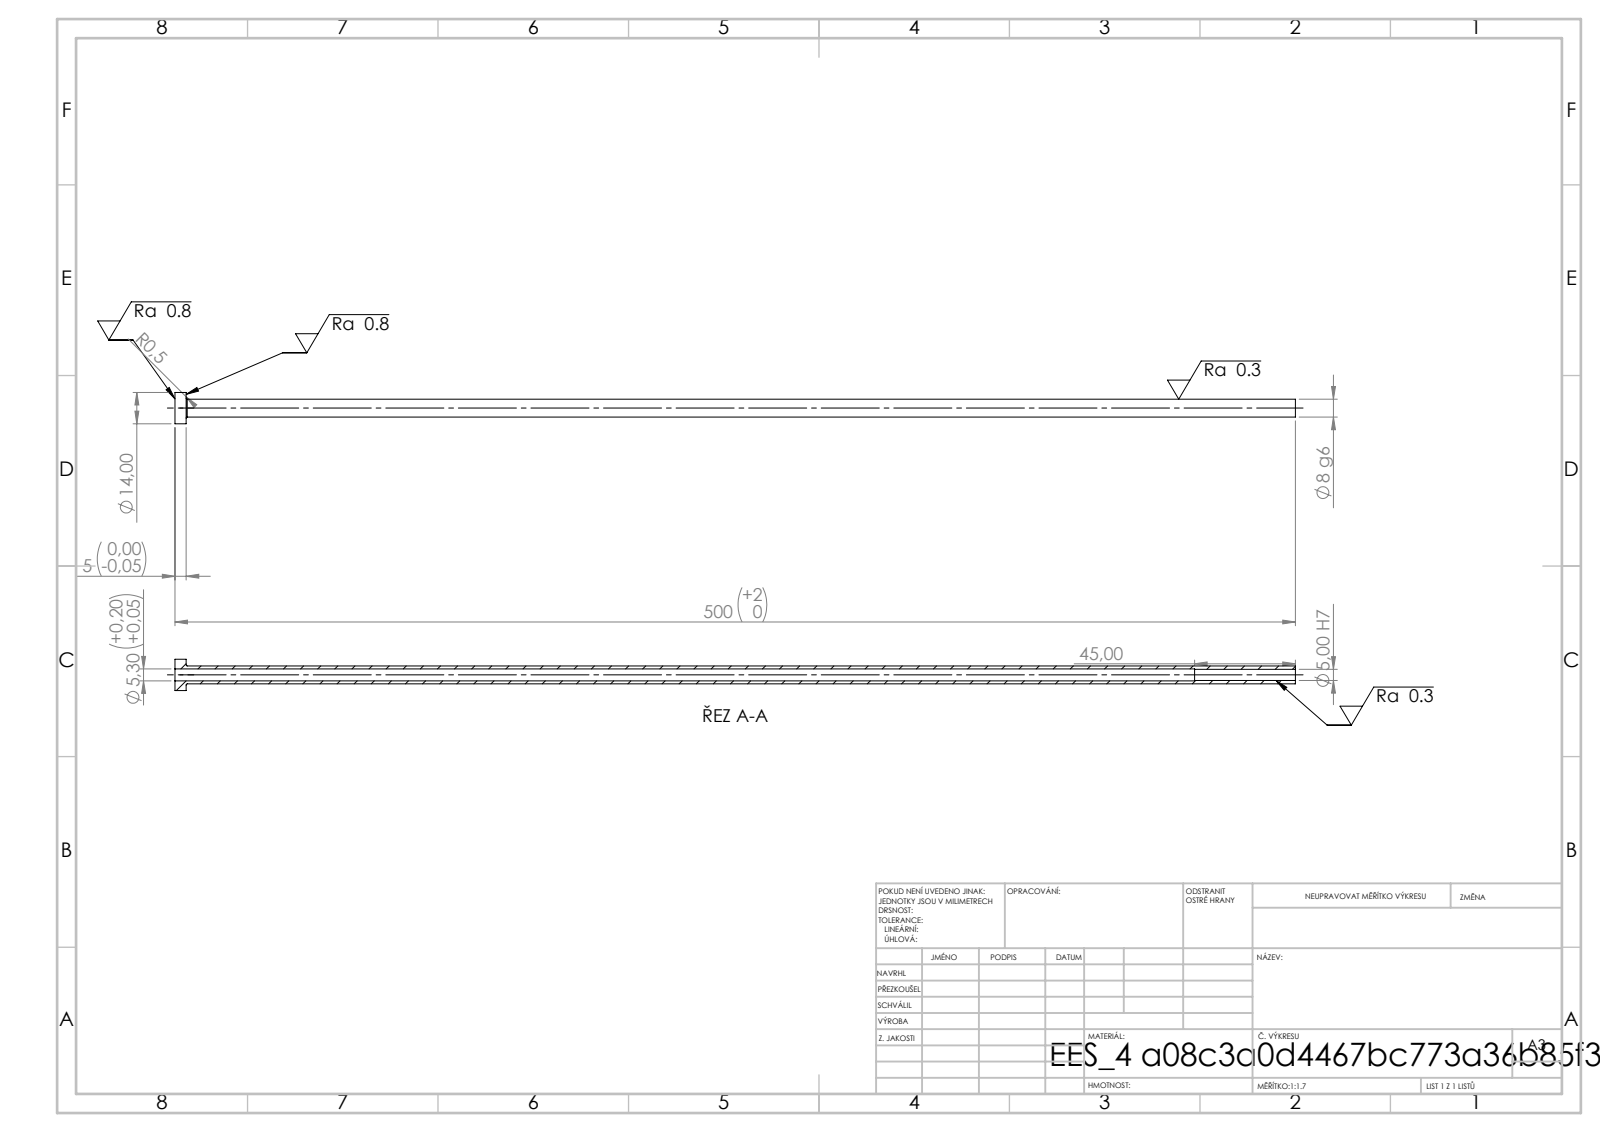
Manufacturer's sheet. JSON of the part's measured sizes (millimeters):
{"step_written_by": "SolidWorks 2019 (CONFIG_CONTROL_DESIGN)", "units": "millimeters", "bodies": {"solids": 1, "faces": 14, "planar": 4, "cylindrical": 8, "other": 2}, "overall_size": [500, 14, 14], "volume_mm3": 14731, "surface_area_mm2": 21207, "round_holes": [[5, 1], [5.3, 1]], "round_bosses_or_shafts": [[14, 1], [8, 1]], "face_to_face_distances": [5, 500, 495, 455, 450, 45]}
